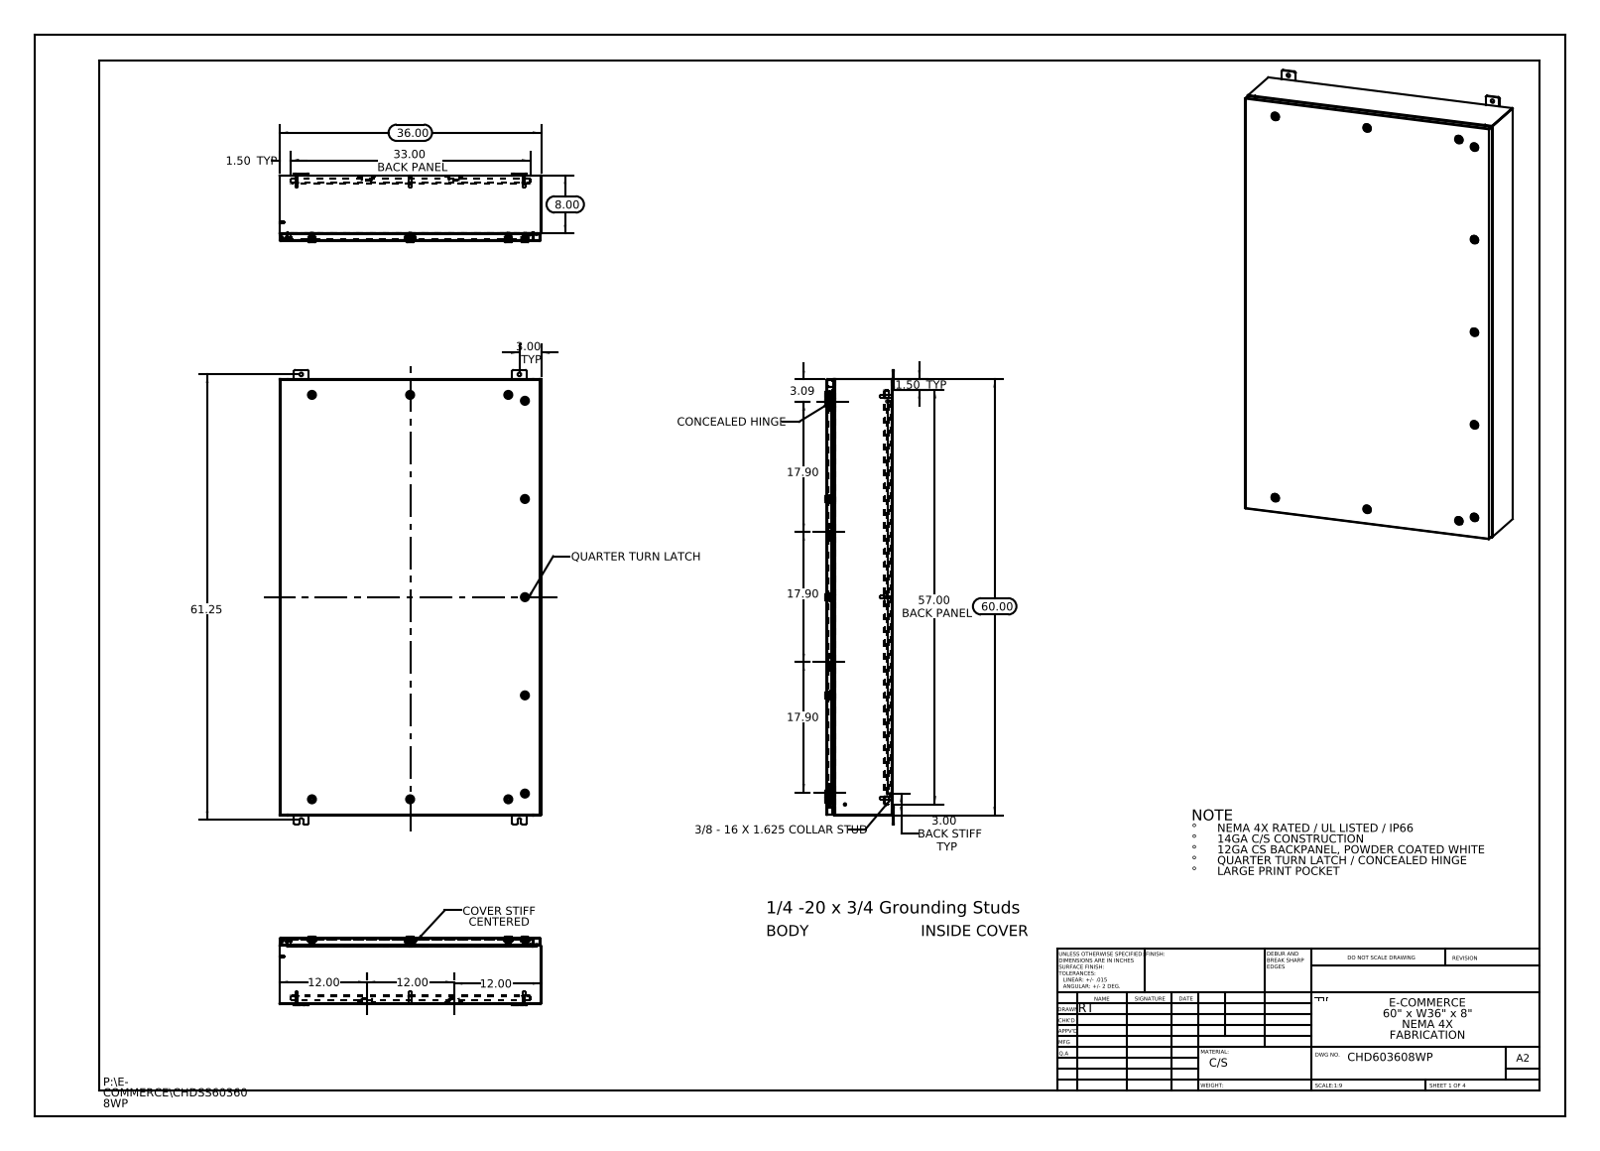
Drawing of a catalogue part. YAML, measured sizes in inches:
part_name: "Quarter-20 CD Stud; CHDSS603608WP Mounting Feet; Concealed Hinge enclosure side; CHDSS603608WP Mounting Studs (+8 more)"
step_written_by: "SolidWorks 2013 (CONFIG_CONTROL_DESIGN)"
units: inches
bodies: {solids: 104, faces: 9960, planar: 2880, cylindrical: 3110, other: 3970}
overall_size: [62.5, 36, 9.356]
volume: 740.9
surface_area: 18271
round_holes:
  - {diameter: 0.5, count: 12}
  - {diameter: 0.197, count: 11}
  - {diameter: 0.394, count: 11}
  - {diameter: 0.4, count: 11}
  - {diameter: 0.63, count: 11}
  - {diameter: 0.787, count: 11}
  - {diameter: 0.136, count: 8}
  - {diameter: 0.25, count: 8}
  - {diameter: 0.211, count: 1}
round_bosses_or_shafts:
  - {diameter: 0.236, count: 13}
  - {diameter: 1.102, count: 11}
  - {diameter: 0.78, count: 11}
  - {diameter: 0.626, count: 11}
  - {diameter: 0.61, count: 11}
  - {diameter: 0.531, count: 11}
  - {diameter: 0.392, count: 11}
  - {diameter: 0.114, count: 11}
partial_cylinders:
  - {radius: 0.006, count: 363}
  - {radius: 0.118, count: 363}
  - {radius: 0.028, count: 132}
  - {radius: 0.02, count: 44}
  - {radius: 0.197, count: 44}
  - {radius: 0.013, count: 34}
  - {radius: 0.088, count: 30}
  - {radius: 0.19, count: 24}
face_to_face_distances: [0.075, 0.074, 8.861, 8.936, 9.01, 8.935, 0.104, 1, 1.075, 7.861]
hole_center_spacings: [13.5, 17.896, 0.688, 2.224, 27, 27.625, 35.791, 41.709]
